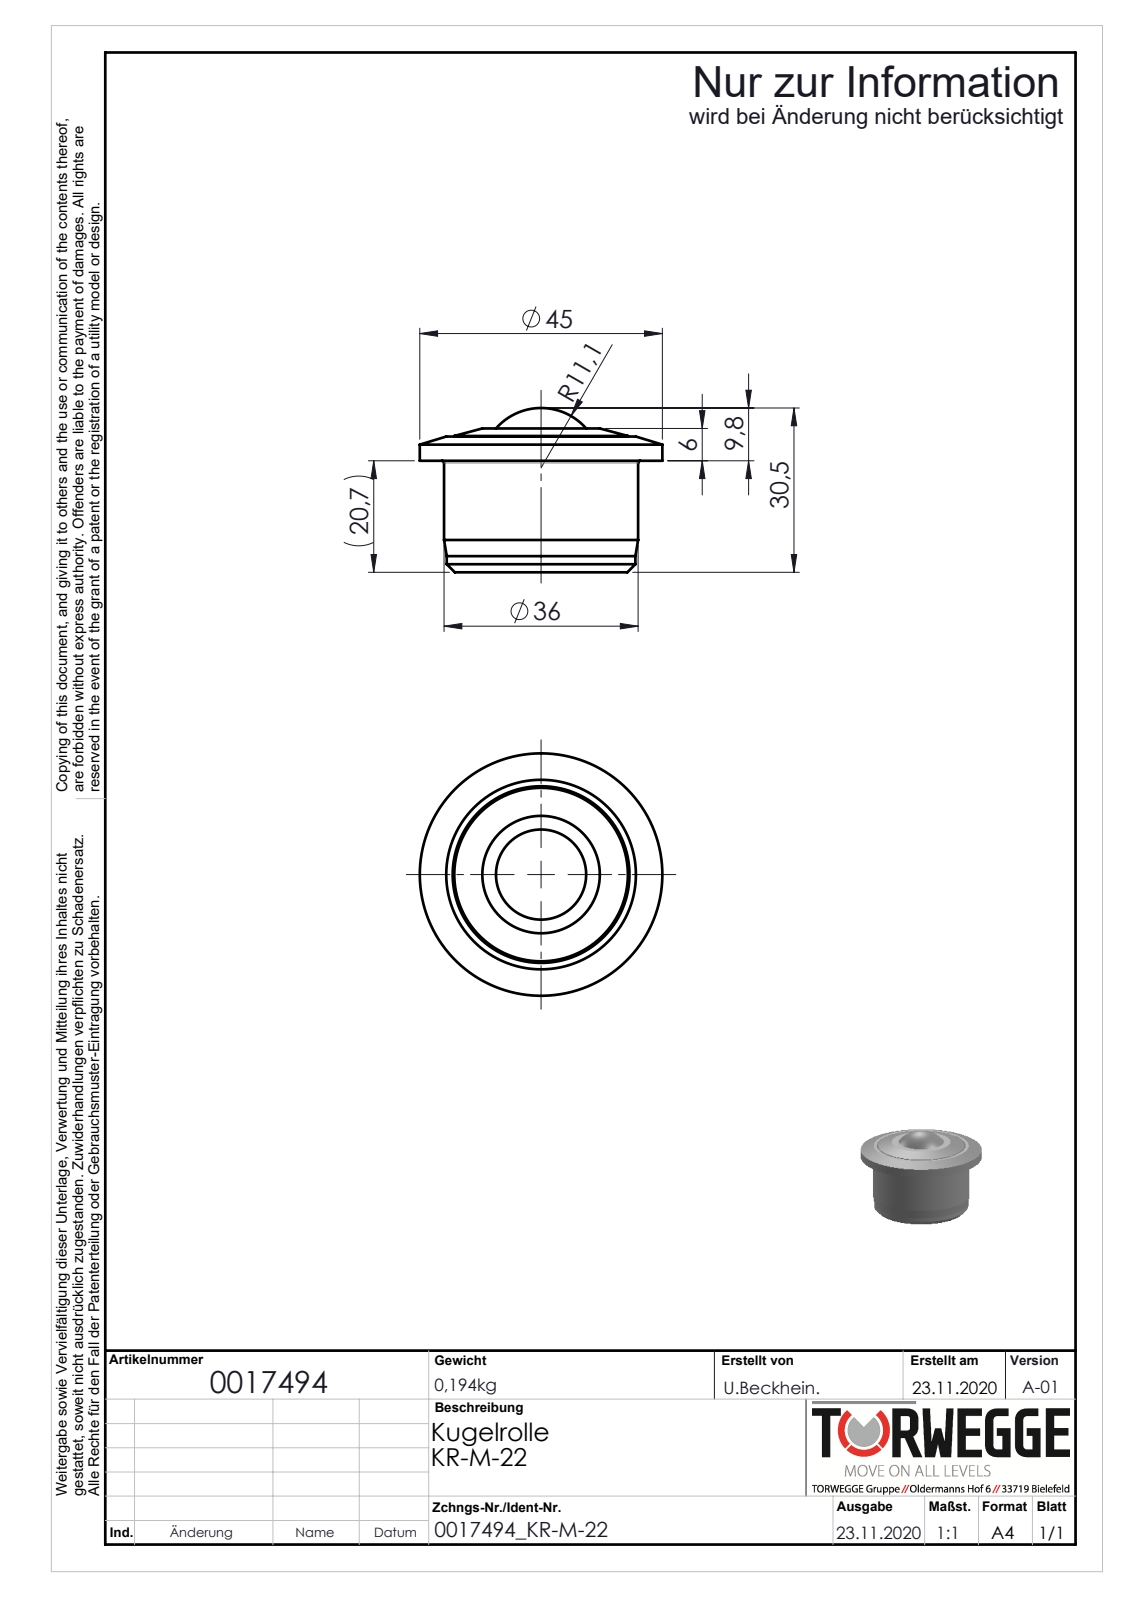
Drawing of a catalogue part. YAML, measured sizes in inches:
part_name: "0017494"
step_written_by: "SolidWorks 2018 (AUTOMOTIVE_DESIGN)"
units: inches
bodies: {solids: 1, faces: 27, planar: 5, cylindrical: 10, other: 12}
overall_size: [1.772, 1.772, 1.201]
volume: 1.749
surface_area: 9.593
round_holes:
  - {diameter: 1.291, count: 1}
round_bosses_or_shafts:
  - {diameter: 1.772, count: 1}
  - {diameter: 1.417, count: 1}
  - {diameter: 1.378, count: 1}
  - {diameter: 1.268, count: 1}
face_to_face_distances: [0.815, 1.051, 0.236, 0.992, 0.177, 0.059, 0.929, 0.114, 0.063, 0.122]
